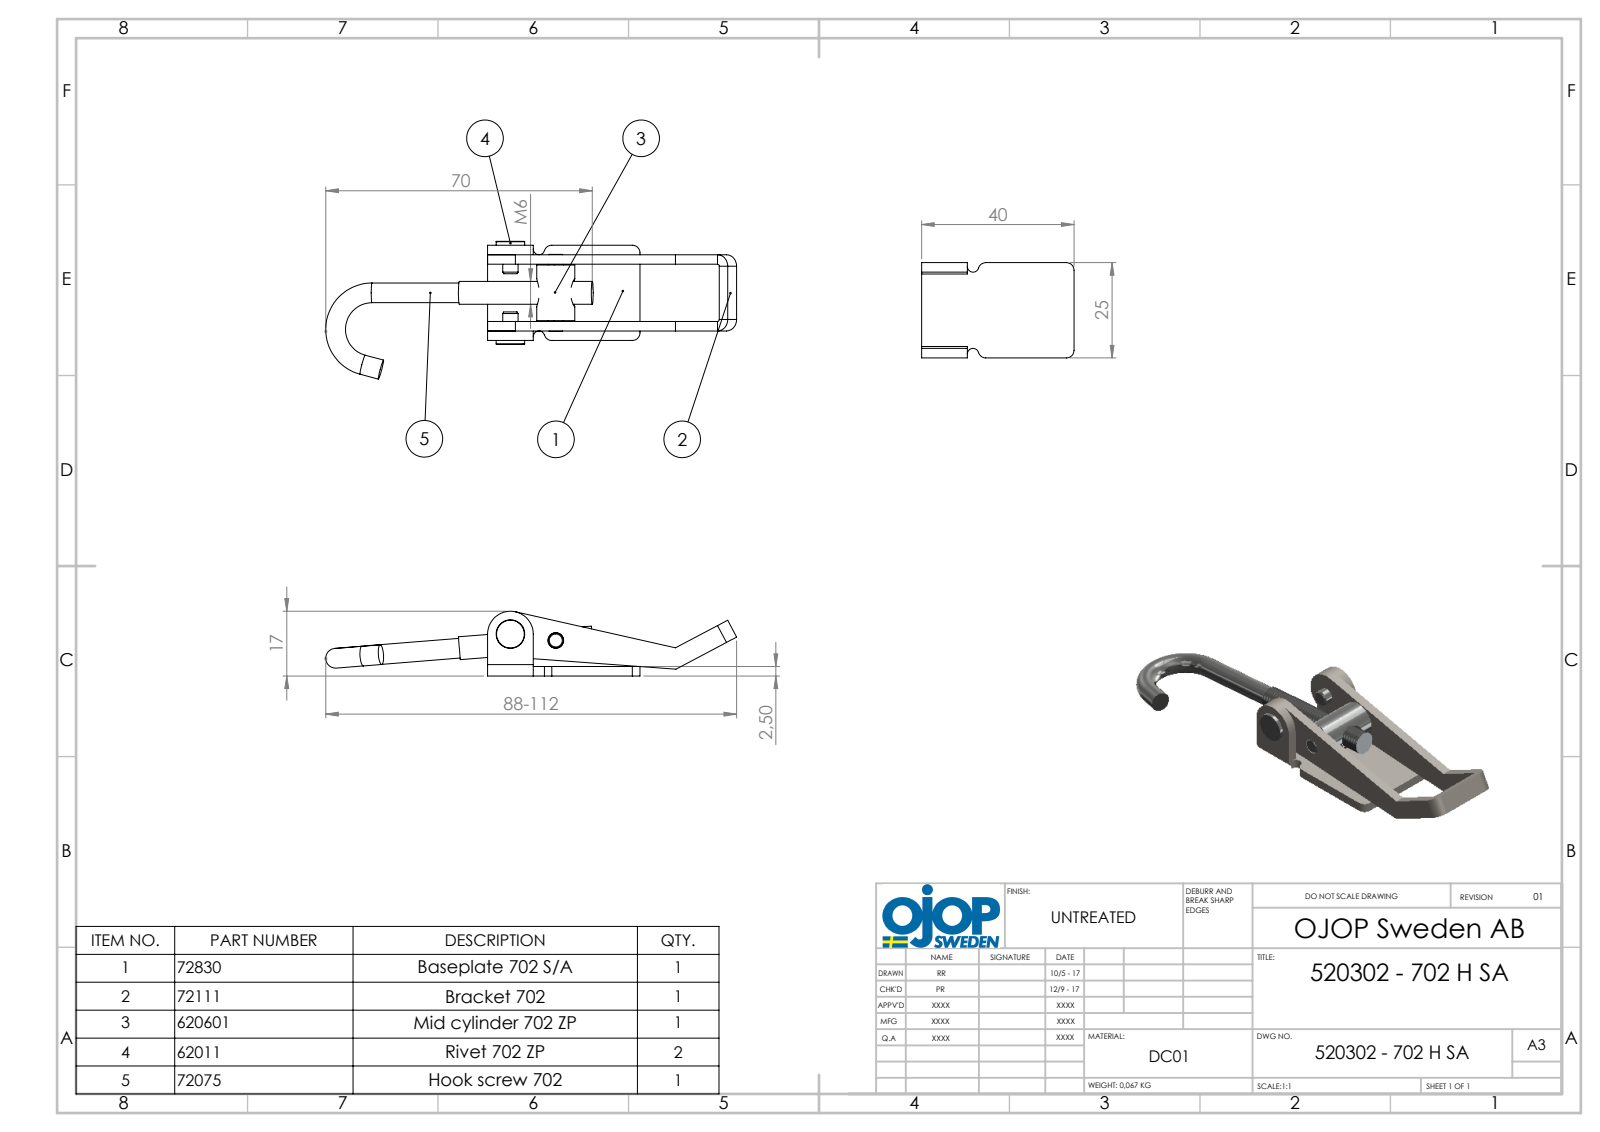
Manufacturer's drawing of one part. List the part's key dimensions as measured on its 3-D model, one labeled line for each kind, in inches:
Part name (STEP PRODUCT): 702 - Ansatsnit; 702 - Rulle; 702 - Hake M6; 520302 - 702 H SA (+2 more)
STEP written by: SolidWorks 2015 (AUTOMOTIVE_DESIGN)
Units: inches
Bodies: 6 solids, 130 faces (55 planar, 57 cylindrical, 18 other)
Overall size (bounding box): 4.246 × 1.423 × 0.669
Volume: 0.565 in³ · Surface area: 13.75 in²
Round holes (diameter × count): ⌀0.161 ×2, ⌀0.197 ×1, ⌀0.236 ×1
Round bosses / shafts (diameter × count): ⌀0.204 ×2, ⌀0.157 ×2, ⌀0.394 ×1, ⌀0.295 ×1, ⌀0.236 ×1
Partial cylindrical surfaces — rounded edges, fillets, slot ends (radius × count): R0.02 ×4, R0.079 ×4, R0.118 ×4, R0.059 ×2, R0.236 ×1
Main face-to-face distances: 0.098, 0.787, 0.689, 0.591, 0.197, 0.886, 0.984, 0.78, 0.205, 0.106
Hole centre spacings: 0.474
